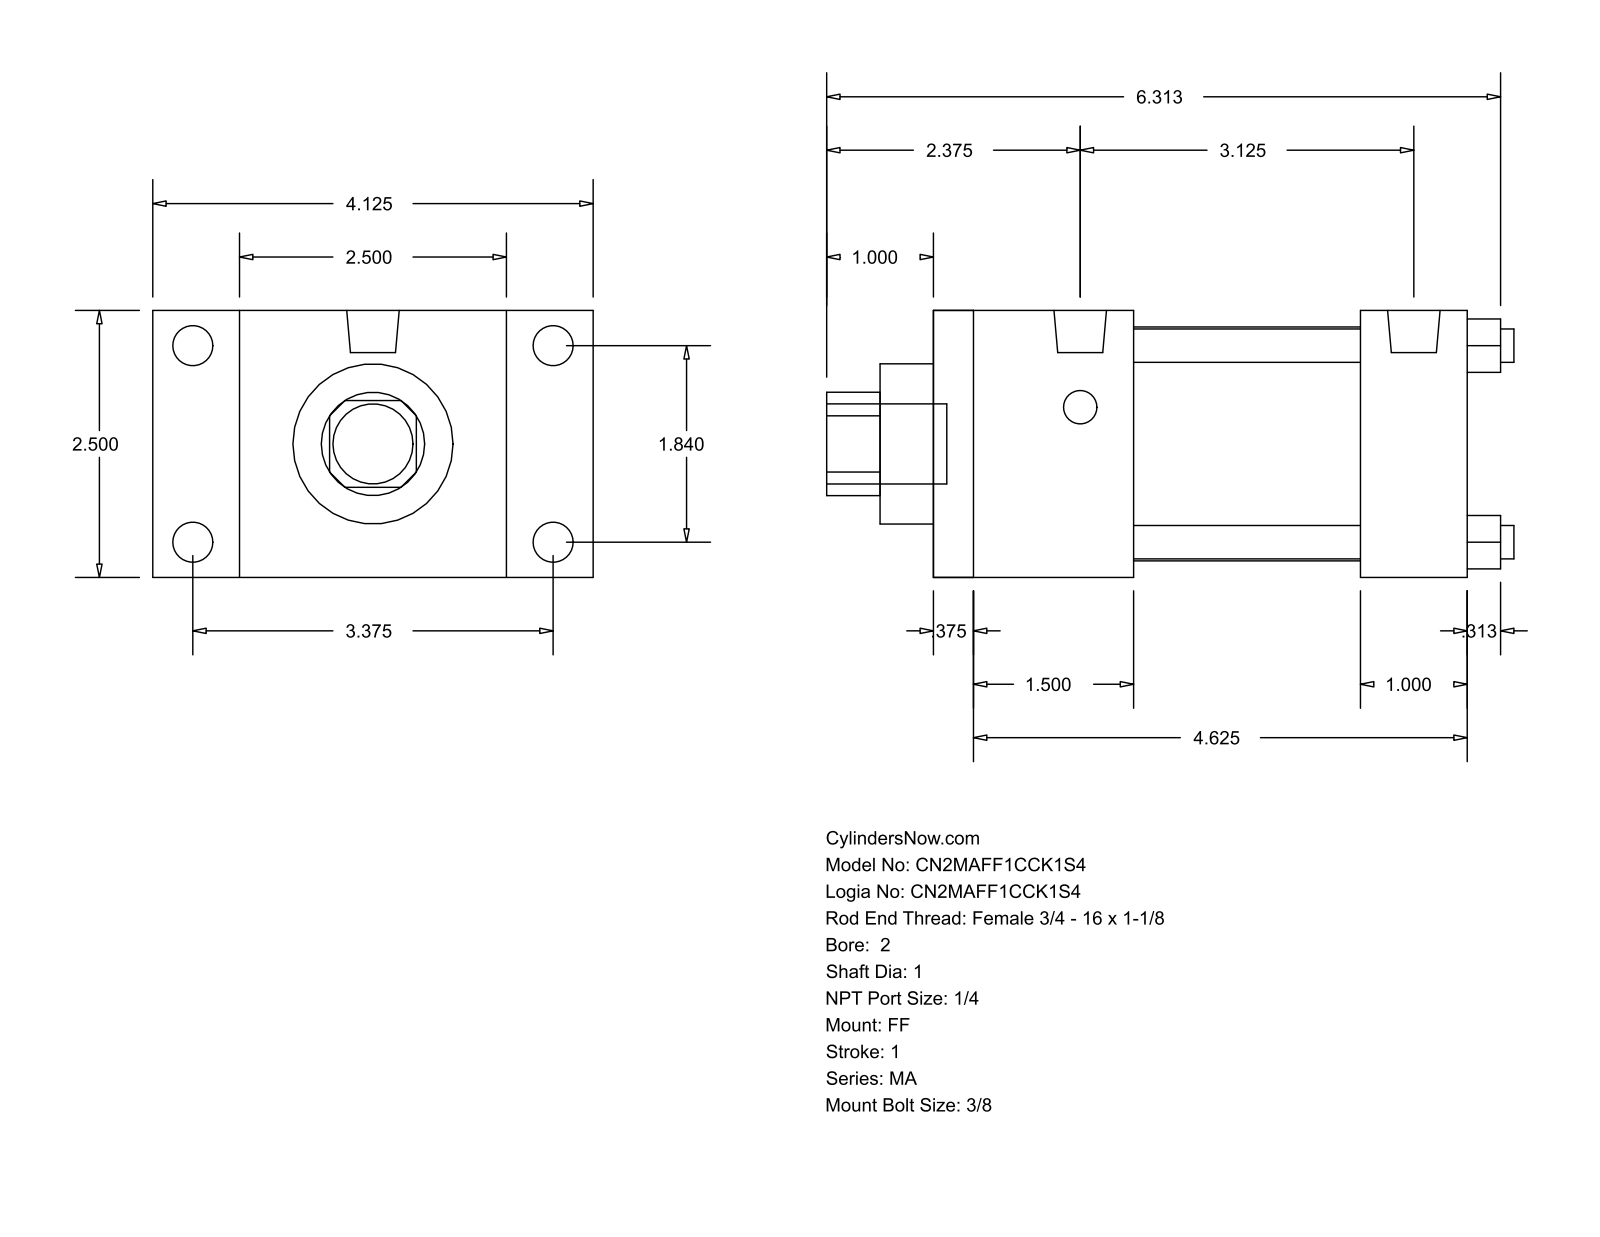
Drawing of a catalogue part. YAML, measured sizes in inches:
part_name: "MA_FF__0200_1"
step_written_by: "GSSL Pune (CONFIG_CONTROL_DESIGN)"
units: inches
bodies: {solids: 0, faces: 92, planar: 64, cylindrical: 28, other: 0}
overall_size: [6.437, 4.125, 2.5]
round_holes:
  - {diameter: 0.313, count: 4}
  - {diameter: 1, count: 1}
  - {diameter: 1.5, count: 1}
  - {diameter: 2.19, count: 1}
round_bosses_or_shafts:
  - {diameter: 0.375, count: 4}
  - {diameter: 0.313, count: 4}
  - {diameter: 0.492, count: 2}
  - {diameter: 0.75, count: 1}
partial_cylinders:
  - {radius: 0.484, count: 1}
face_to_face_distances: [2.5, 5, 0.375, 4.625, 1, 0.813, 0.5, 1.875, 4, 1.5]
hole_center_spacings: [1.301, 1.84, 2.602]
